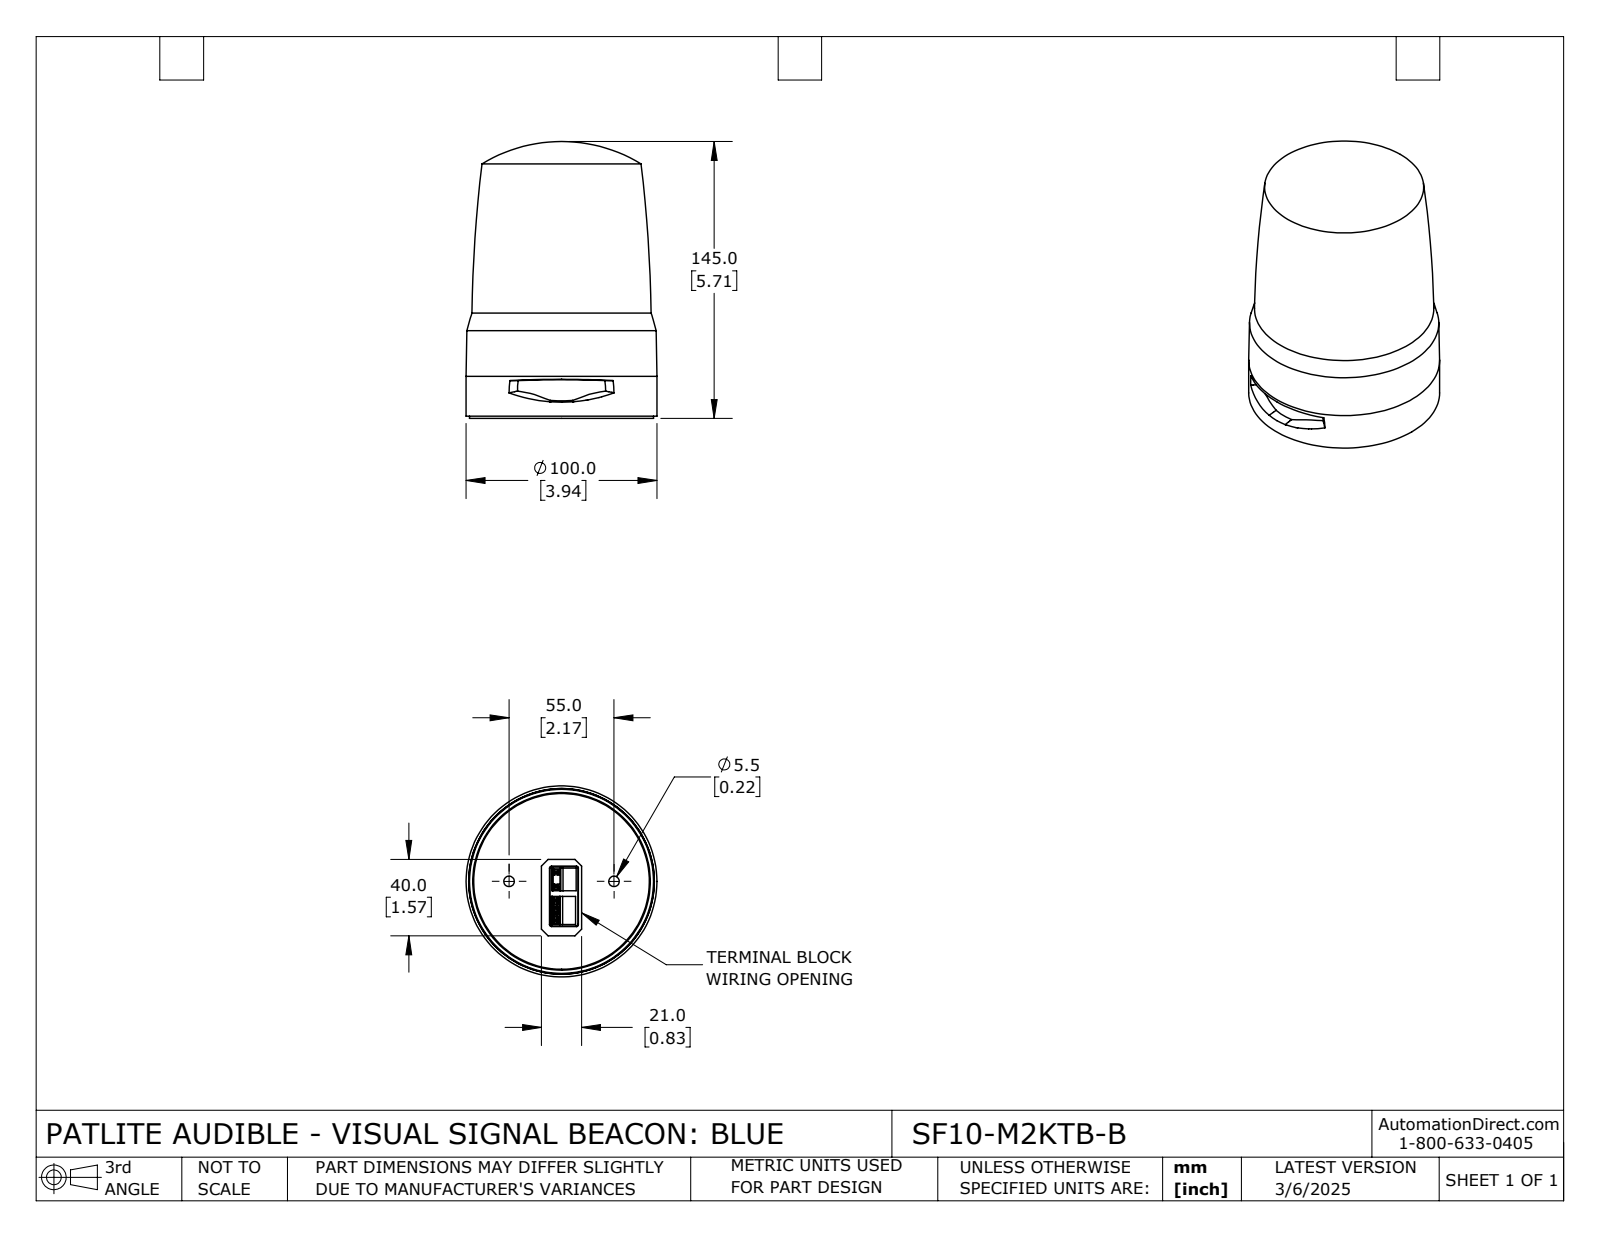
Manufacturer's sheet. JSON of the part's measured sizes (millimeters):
{"part_name": "SF10-M2KTB-B", "step_written_by": "SolidWorks 2024 (CONFIG_CONTROL_DESIGN)", "units": "millimeters", "bodies": {"solids": 2, "faces": 275, "planar": 174, "cylindrical": 31, "other": 70}, "overall_size": [145, 100, 100], "volume_mm3": 875277, "surface_area_mm2": 79857, "round_holes": [[5.5, 2], [13, 2], [93, 1]], "round_bosses_or_shafts": [[100, 1], [96.4, 1], [94.5, 1], [93.2, 1], [92, 1]], "partial_cylinders_radius": [[1, 4], [0.3, 2], [44.75, 1], [45, 1]], "face_to_face_distances": [6.3, 18.2, 11.9, 5.6, 12.6, 5.1, 0.4, 4.7, 1.2, 17], "hole_center_spacings": [27.5, 55]}
